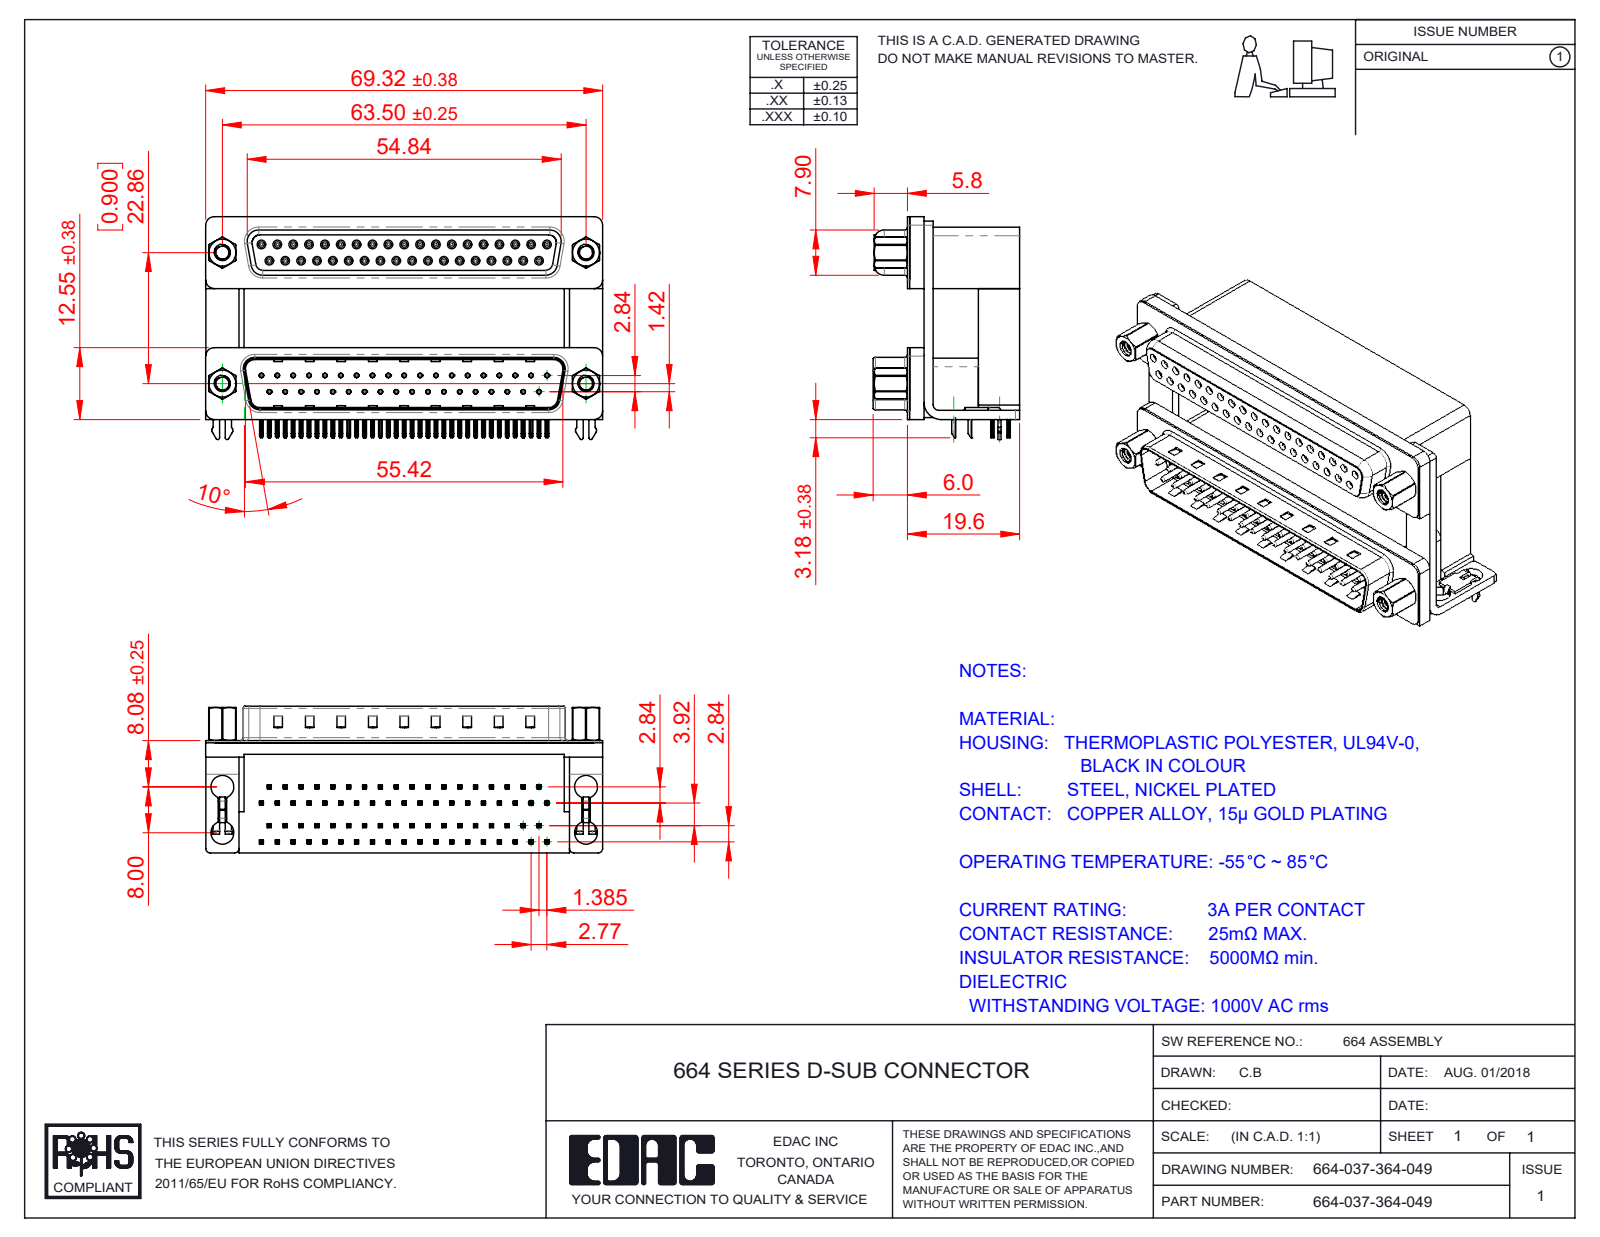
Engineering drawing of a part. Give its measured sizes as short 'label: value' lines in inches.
name: 664 Shell Plug_37 Contacts; 664-037-364-049; 664 Housing Spacer_37 Contacts H; 664 Contact Bottom Upper_H (+8 more)
written by: SolidWorks 2020 (CONFIG_CONTROL_DESIGN)
unit: in
bodies: 91 solids, 9305 faces (4863 planar, 2351 cylindrical, 2091 other)
size: 2.729 × 1.532 × 1.008
volume: 2.02 in³; area: 54.57 in²
holes: 74× ⌀0.031, 37× ⌀0.014, 37× ⌀0.035, 8× ⌀0.157, 4× ⌀0.089, 4× ⌀0.09, 4× ⌀0.138, 4× ⌀0.189, 4× ⌀0.197
bosses: 37× ⌀0.047, 37× ⌀0.03, 4× ⌀0.193, 4× ⌀0.187, 4× ⌀0.154, 4× ⌀0.11
rounds: 297× R0.004, 154× R0.01, 148× R0.006, 74× R0.005, 74× R0.014, 37× R0.013, 18× R0.011, 16× R0.02
face distances: 0.016, 0.756, 0.472, 0.283, 0.086, 0.112, 0.026, 0.886, 0.488, 0.421
hole spacings: 0.109, 0.218, 0.124, 0.327, 0.436, 0.545, 0.654, 0.763
